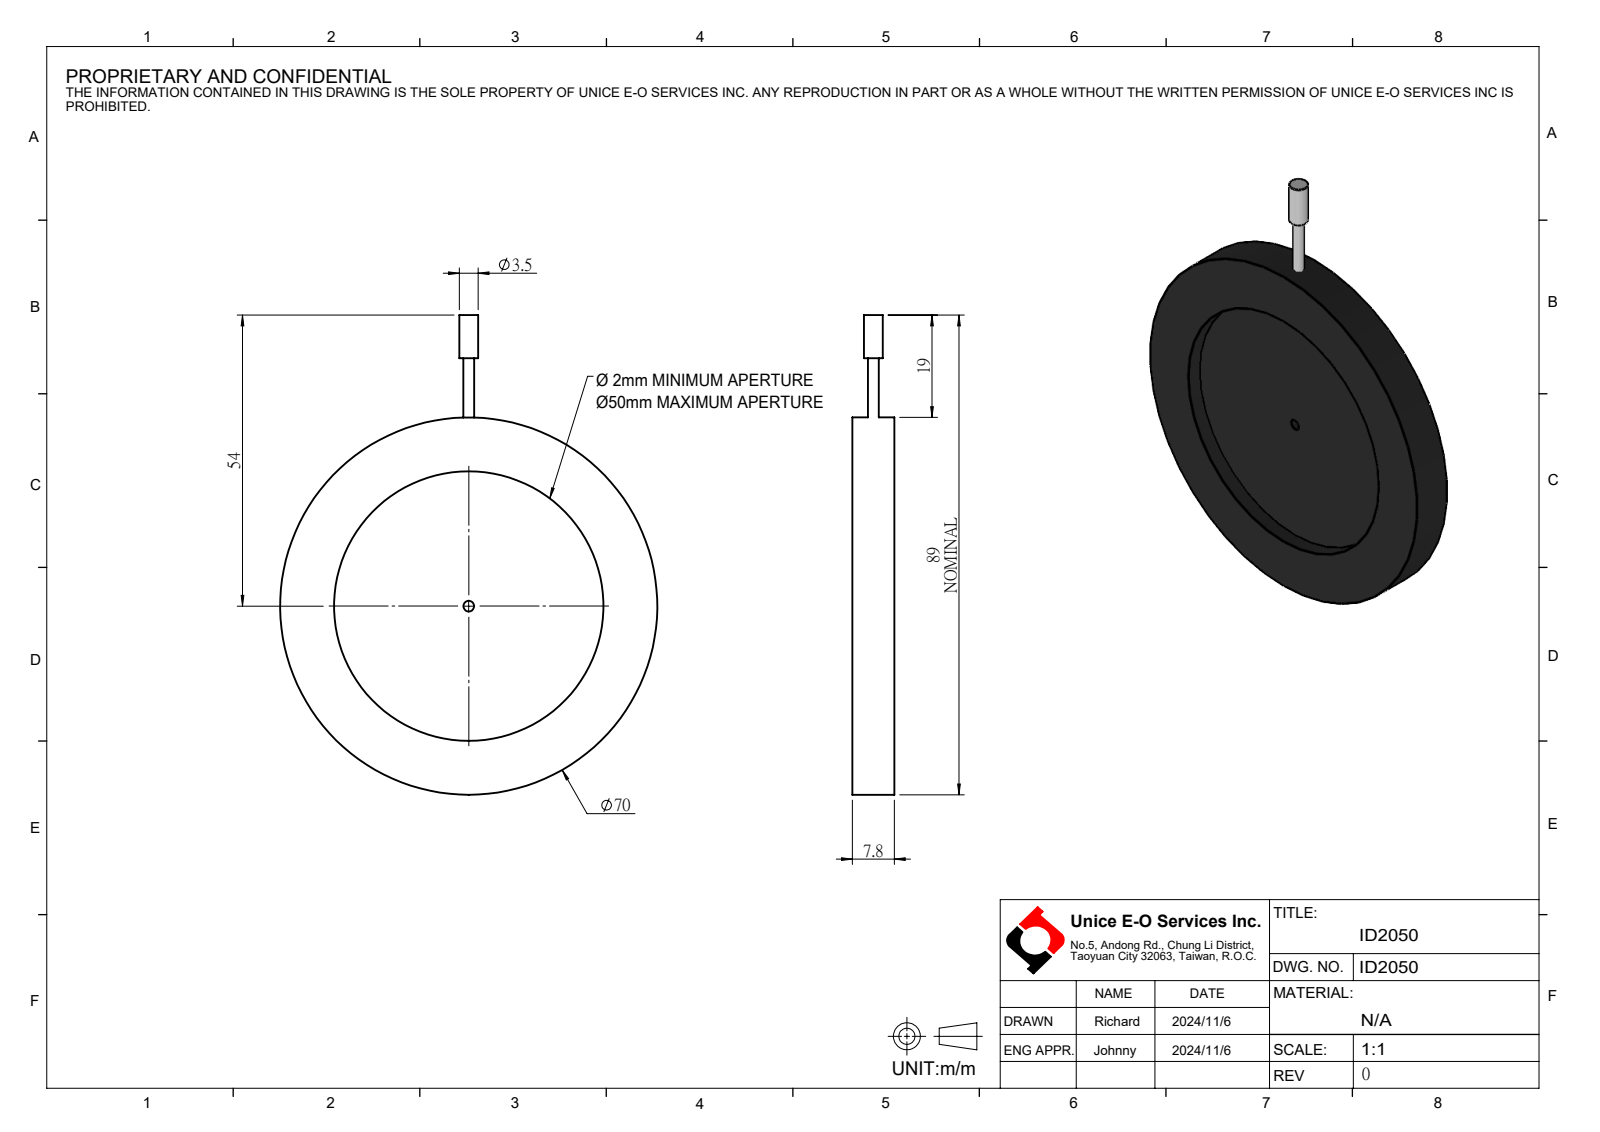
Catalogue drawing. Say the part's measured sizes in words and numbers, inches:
The part is named "ID2050". Its 3-D file was written by "SolidWorks 2024 (AUTOMOTIVE_DESIGN)". It is 2 solids with 19 faces: 7 planar, 12 cylindrical and 0 other. Overall it measures 3.504 by 2.756 by 0.307 inches. Its volume is 1.12 cubic inches and its surface area 16.34 square inches. Round holes: 1 of diameter 0.079, 1 of diameter 1.969. Round bosses or shafts: 1 of diameter 2.756, 1 of diameter 0.138, 1 of diameter 0.079. The main face-to-face distances are 0.118, 0.189, 0.071, 0.307, 0.315, 0.787, 0.472.
